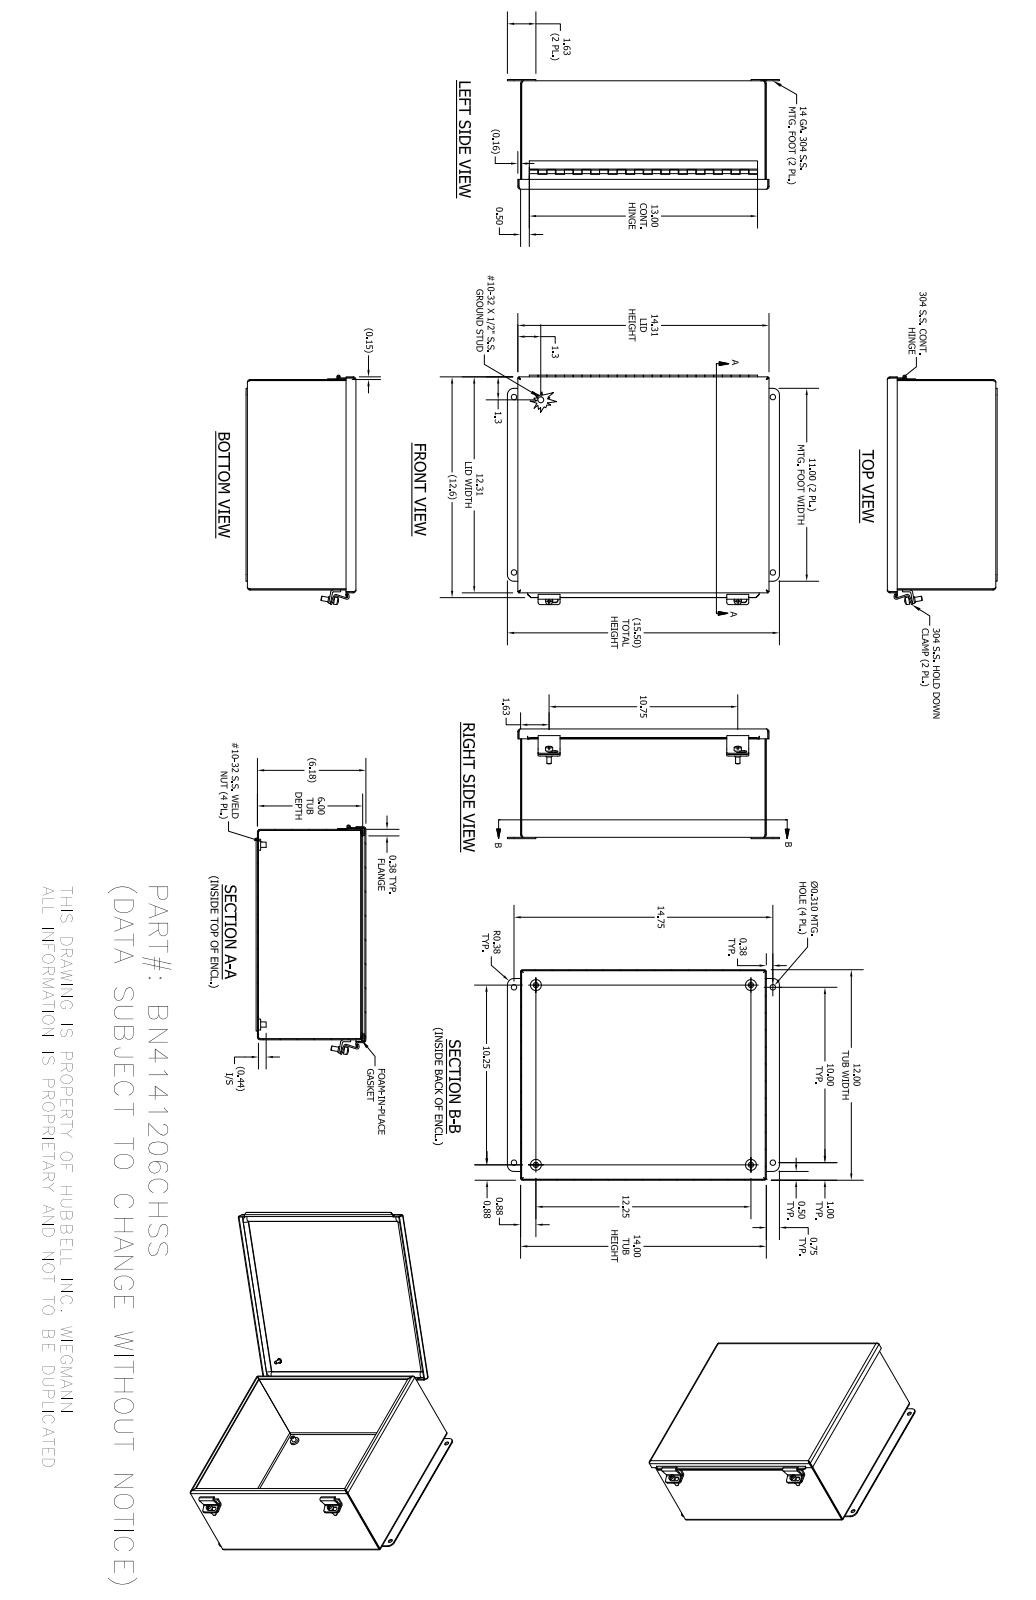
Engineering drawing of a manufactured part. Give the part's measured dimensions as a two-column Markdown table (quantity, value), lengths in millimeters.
| quantity | value |
| --- | --- |
| part name | B_141206_SSBKP; H4050553LH; H4050553P; H4050553TH (+8 more) |
| STEP written by | Autodesk Inventor 2016 (AUTOMOTIVE_DESIGN) |
| units | millimeters |
| bodies | 19 solids, 488 faces (268 planar, 153 cylindrical, 67 other) |
| overall size | 393.7 × 332.38 × 158.91 |
| volume | 811 006 mm³ |
| surface area | 1 027 000 mm² |
| round holes (diameter × count) | 2.79 × 4, 3.96 × 4, 7.87 × 4, 4.98 × 2, 2.96 × 1 |
| round bosses / shafts (diameter × count) | 15.88 × 4, 7.62 × 4, 10.4 × 2, 8.74 × 2, 6.35 × 2, 8.56 × 1, 5.08 × 1, 4.83 × 1 |
| partial cylindrical surfaces (radius × count) | 2.38 × 13, 3.88 × 13, 1.68 × 8, 3.17 × 8, 3.38 × 4, 5.78 × 4, 9.53 × 4, 1.6 × 3 |
| main face-to-face distances | 1.5, 155.51, 157.01, 154.01, 303.3, 354.1, 304.8, 301.8, 355.6, 352.6 |
| hole center spacings | 31.9, 254, 273.05, 342.91, 19.05, 259.12, 259.13, 260.35 |
